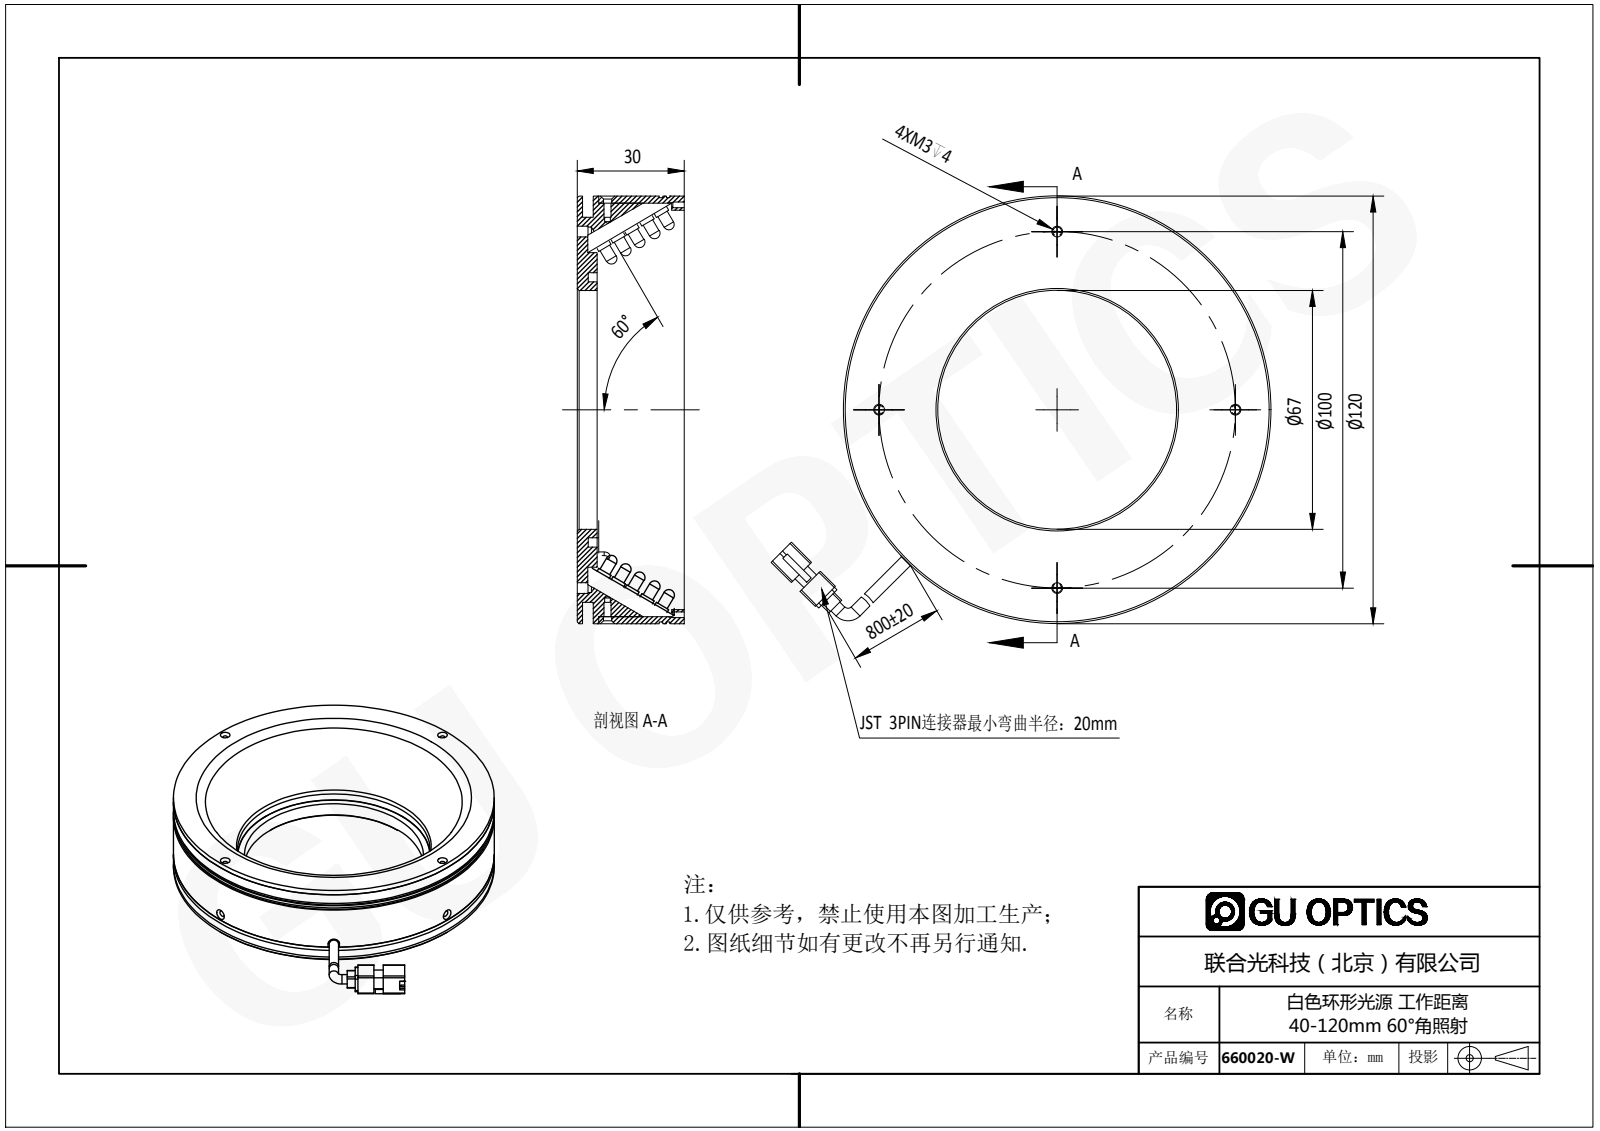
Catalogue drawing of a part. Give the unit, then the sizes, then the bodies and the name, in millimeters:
Units: millimetres
Overall size (bounding box): 140.26 × 120 × 32
Round holes (diameter × count): ⌀1.6 ×6, ⌀3.5 ×5, ⌀1.25 ×4, ⌀1.7 ×4, ⌀3 ×4, ⌀2 ×2, ⌀2.3 ×2, ⌀67 ×1, ⌀72 ×1, ⌀77 ×1, ⌀112 ×1
Round bosses / shafts (diameter × count): ⌀3.8 ×350, ⌀3 ×350, ⌀3.5 ×2, ⌀120 ×1, ⌀119 ×1, ⌀116 ×1, ⌀108 ×1, ⌀88.2 ×1
Partial cylindrical surfaces — rounded edges, fillets, slot ends (radius × count): R0.5 ×8, R1 ×4, R1.25 ×4, R1.65 ×1, R10 ×1
Main face-to-face distances: 30, 1.5, 4.5, 2, 3, 32, 25.5, 28.5, 30.5, 27.5
Hole centre spacings: 76.2, 7.5, 50, 57.5, 70.71, 81.32, 107.5, 100
Volume: 107 797 mm³ · Surface area: 124 847 mm²
Bodies: 356 solids, 6266 faces (4293 planar, 1552 cylindrical, 421 other)
Part name (STEP PRODUCT): 660020-W
STEP written by: SolidWorks 2016 (AUTOMOTIVE_DESIGN)
